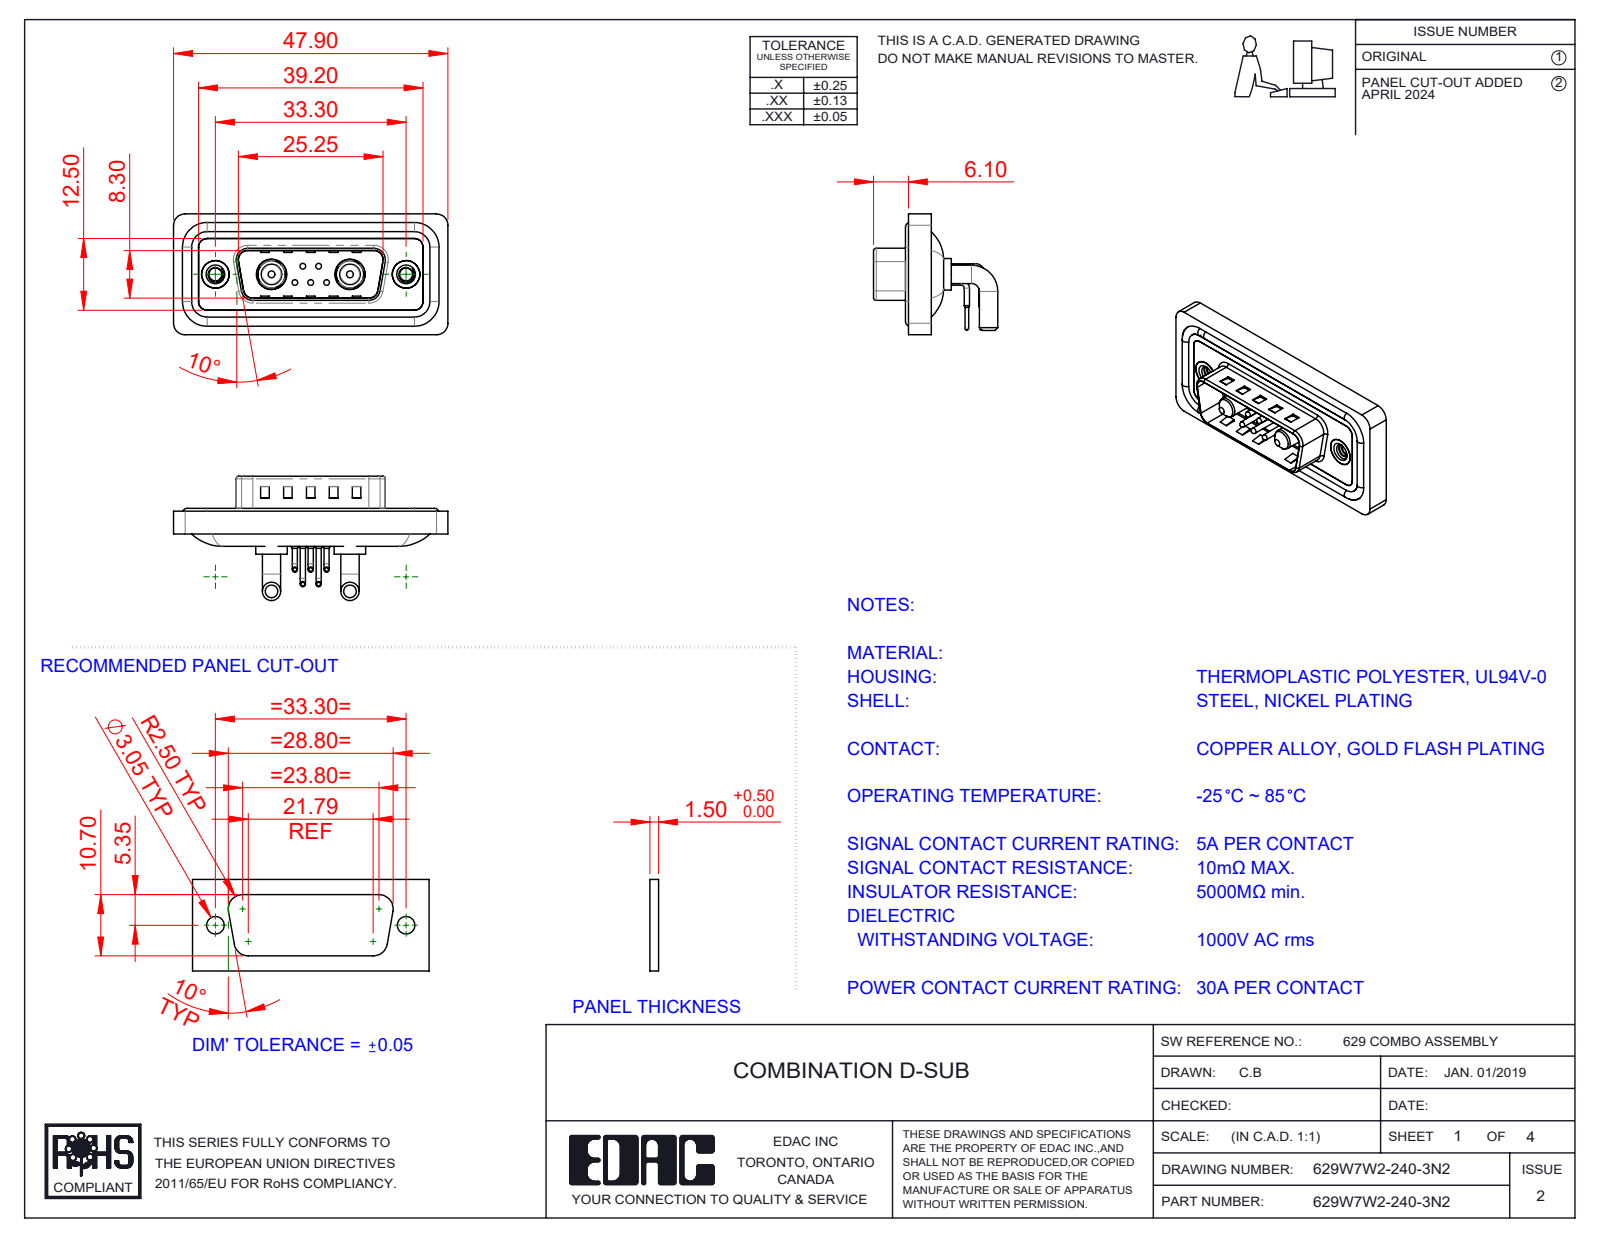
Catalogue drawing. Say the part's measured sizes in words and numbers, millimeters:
The part is named "629Combo Shell Rear_15 Contacts; 629Combo Contact Row 1; 629W7W2-140-3N2; 629Combo Housing_7W2 (+5 more)". Its 3-D file was written by "SolidWorks 2023 (CONFIG_CONTROL_DESIGN)". It is 16 solids with 1083 faces: 517 planar, 406 cylindrical and 160 other. Overall it measures 47.9 by 21.7 by 21.1 millimeters. Its volume is 5 748 cubic millimeters and its surface area 9 178 square millimeters. Round holes: 5 of diameter 0.75, 5 of diameter 1.6, 5 of diameter 2, 2 of diameter 2.26, 2 of diameter 4, 2 of diameter 4.8, 2 of diameter 4.85, 2 of diameter 5, 2 of diameter 5.3. Round bosses or shafts: 10 of diameter 0.9, 5 of diameter 1.5, 5 of diameter 1, 5 of diameter 0.65, 4 of diameter 3.2, 4 of diameter 1.6, 2 of diameter 5.5, 2 of diameter 5.2. Partial cylindrical surfaces (rounded edges, fillets, slot ends): 20 of radius 2, 18 of radius 1.5, 8 of radius 0.5, 8 of radius 1.6, 5 of radius 1.01, 4 of radius 0.25, 4 of radius 0.6, 4 of radius 0.65. The main face-to-face distances are 0.4, 2.9, 0.8, 1.1, 2.1, 1.6, 2.5, 3.1, 4.5, 4.1. The hole center spacings are 3.16, 2.77, 9.8, 23.5, 4.31, 4.33, 5.03, 5.04.
